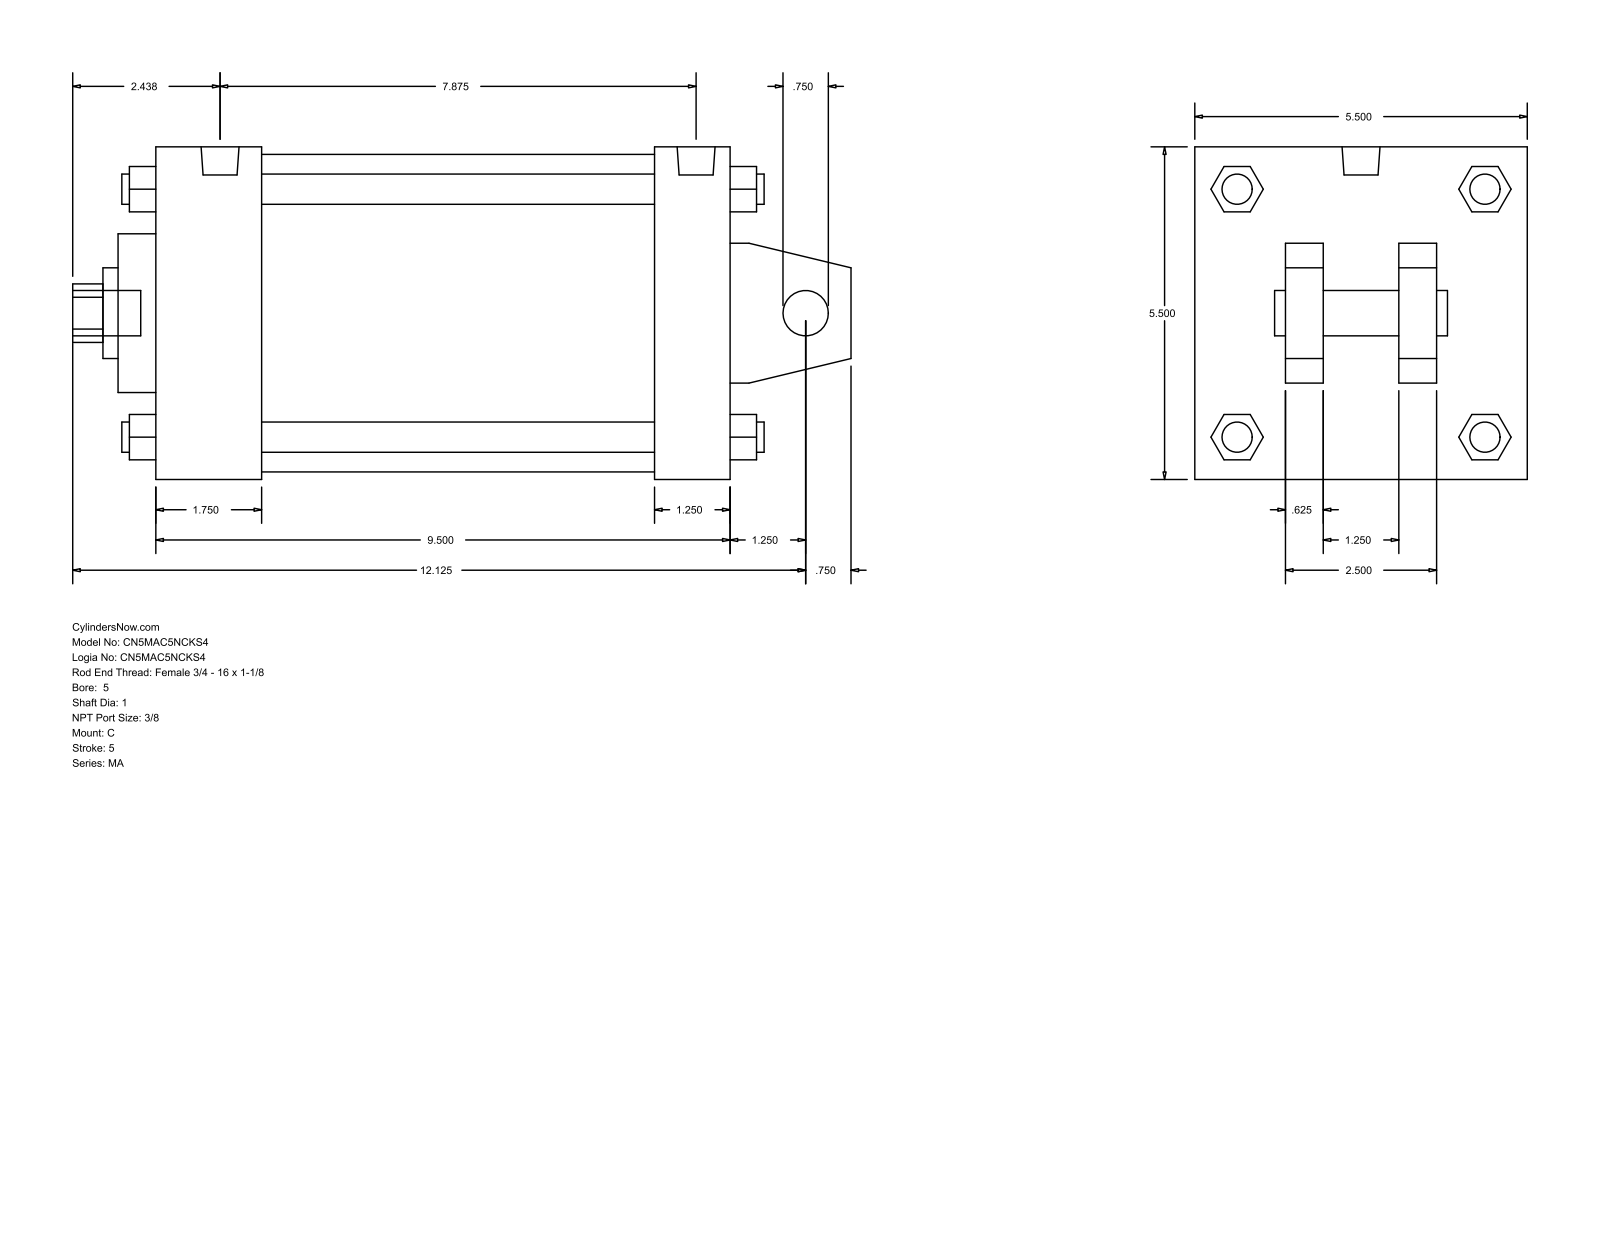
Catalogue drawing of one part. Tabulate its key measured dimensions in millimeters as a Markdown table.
| quantity | value |
| --- | --- |
| part name | MA_C__0500_1 |
| STEP written by | GSSL Pune (CONFIG_CONTROL_DESIGN) |
| units | millimeters |
| bodies | 0 solids, 141 faces (109 planar, 32 cylindrical, 0 other) |
| overall size | 327.02 × 139.7 × 139.7 |
| round holes (diameter × count) | 19.05 × 1, 25.4 × 1, 38.1 × 1, 66.67 × 1, 133.35 × 1 |
| round bosses / shafts (diameter × count) | 12.7 × 4, 11.11 × 4, 15.93 × 2, 19.05 × 1 |
| partial cylindrical surfaces (radius × count) | 12.29 × 1 |
| main face-to-face distances | 139.7, 241.31, 31.76, 15.87, 209.55, 44.46, 165.09, 196.85, 38.1, 101.6 |
